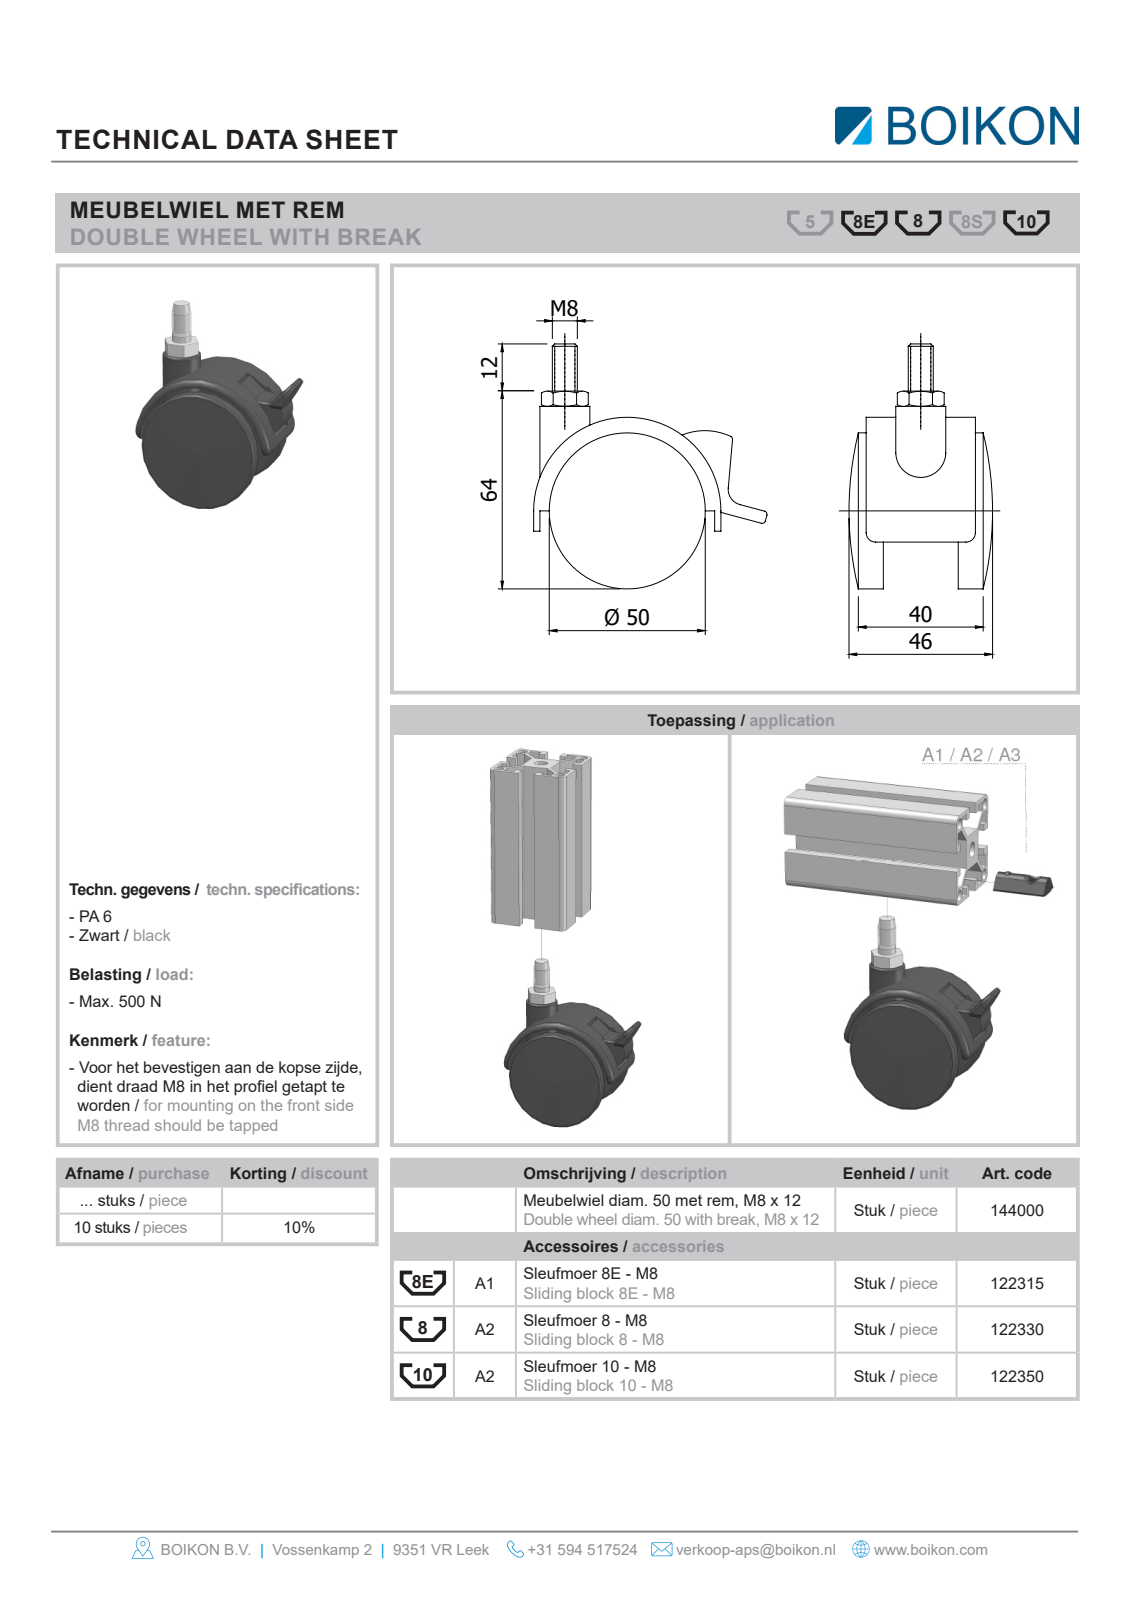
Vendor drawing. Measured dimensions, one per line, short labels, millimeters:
name: Root; 144000Meubelwiel diam 50 rem M8 x 20BOIKON
written by: HiCAD 2013 1802.4 Build 509 (AUTOMOTIVE_DESIGN)
unit: mm
bodies: 1 solid, 26 faces (19 planar, 6 cylindrical, 1 other)
size: 90 × 62.58 × 46
volume: 118 376 mm³; area: 15 552 mm²
bosses: 1× ⌀16, 1× ⌀6.47
rounds: 2× R1.5, 1× R25, 1× R30
face distances: 46, 17, 4, 14.5, 31.5, 10, 30, 20, 29, 19
